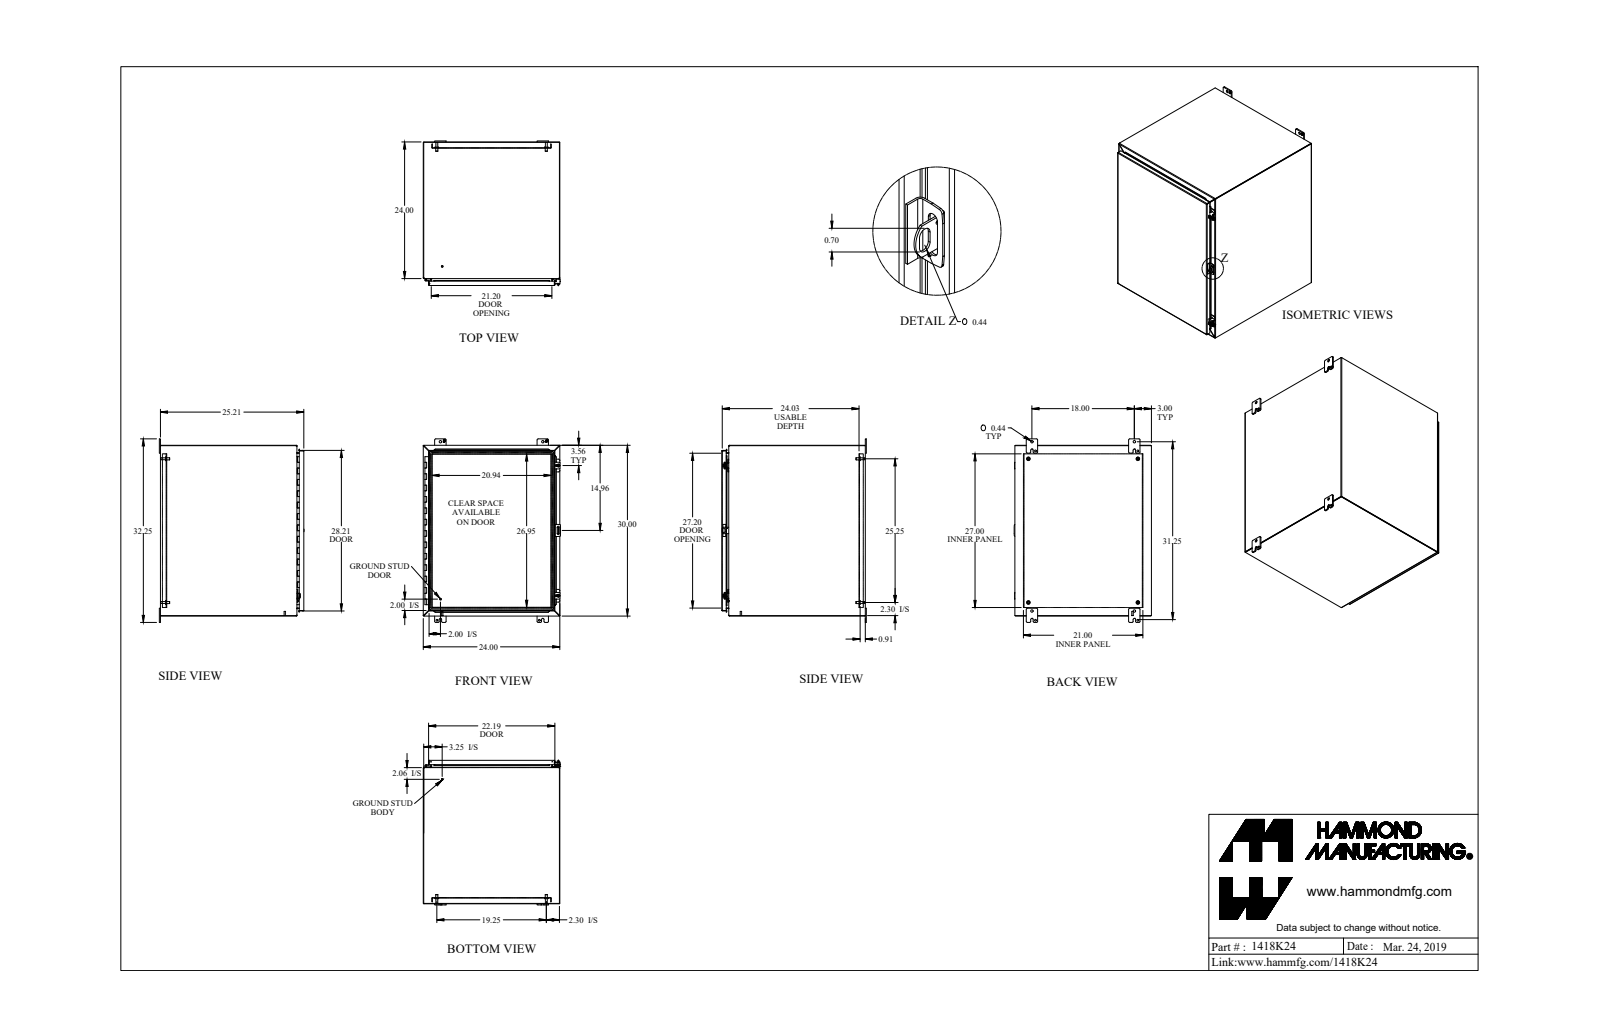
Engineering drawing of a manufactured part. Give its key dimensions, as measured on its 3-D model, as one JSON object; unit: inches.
{"part_name": "1418K24_Default", "step_written_by": "SolidWorks 2019 (CONFIG_CONTROL_DESIGN)", "units": "inches", "bodies": {"solids": 40, "faces": 1203, "planar": 723, "cylindrical": 404, "other": 76}, "overall_size": [32.25, 25.437, 24.125], "volume_in3": 387.1, "surface_area_in2": 10266, "round_holes": [[0.313, 4], [0.437, 4], [0.5, 4], [0.213, 2], [0.265, 2], [0.307, 2], [0.375, 2], [0.125, 1], [0.187, 1], [0.445, 1], [0.445, 1]], "round_bosses_or_shafts": [[0.65, 4], [0.375, 4], [0.33, 4], [1, 2], [0.5, 2], [0.39, 2], [0.281, 2], [0.25, 2]], "partial_cylinders_radius": [[0.188, 26], [0.036, 22], [0.108, 22], [0.048, 13], [0.143, 13], [0.25, 12], [0.04, 8], [0.218, 8]], "face_to_face_distances": [0.072, 23.928, 25.113, 29.928, 24, 23.856, 25.041, 25.185, 0.937, 0.095], "hole_center_spacings": [1.736, 18, 19.25, 29.75, 34.772, 33.837, 2.434, 3.065]}
